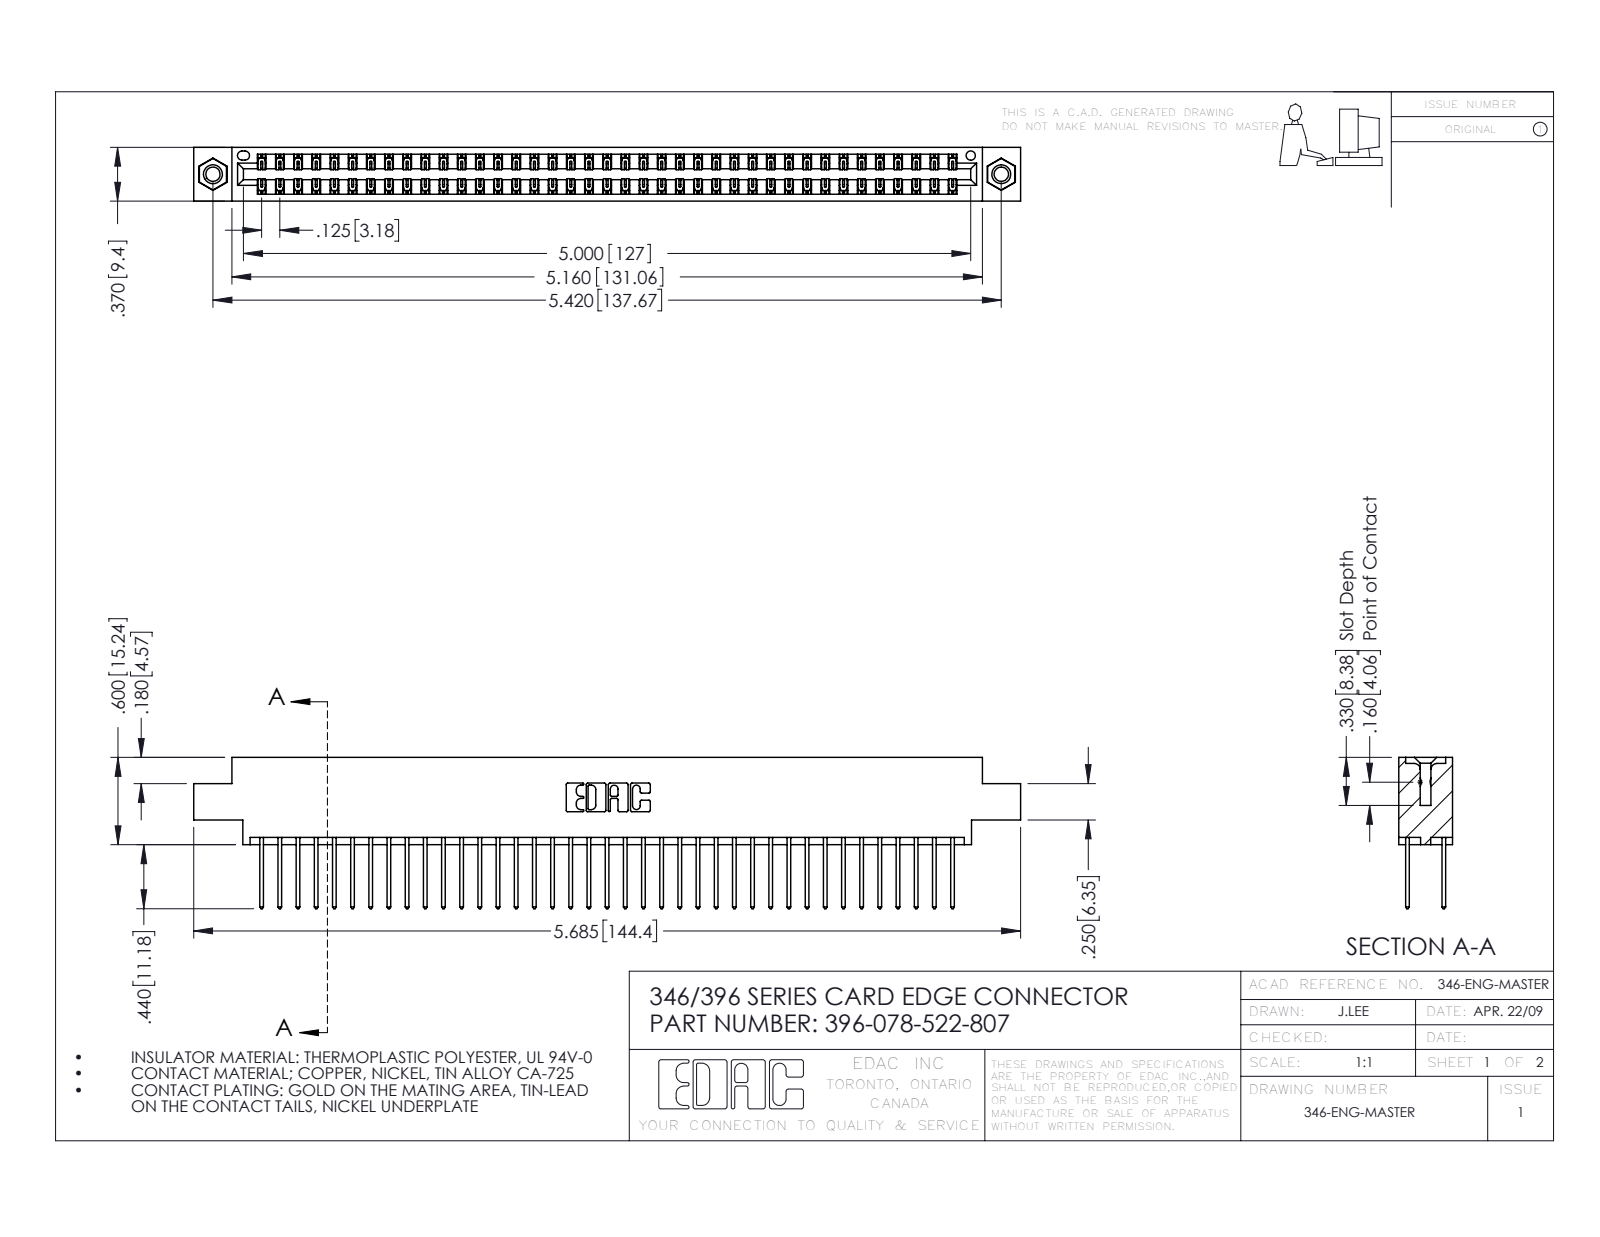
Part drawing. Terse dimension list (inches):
name: 345-292-001_345-293-122; 396-078-522-807; 346 Part_0.170 Offset - 0.156 Dia-TI; 345-250-001_345-250-005-103
written by: SolidWorks 2016 (CONFIG_CONTROL_DESIGN)
unit: in
bodies: 81 solids, 4242 faces (2842 planar, 1384 cylindrical, 16 other)
size: 5.685 × 1.04 × 0.37
volume: 0.86 in³; area: 31.71 in²
holes: 2× ⌀0.098, 2× ⌀0.125, 2× ⌀0.156, 1× ⌀0.064
bosses: 2× ⌀0.155
rounds: 117× R0.006, 78× R0.01, 22× R0.01, 6× R0.007, 6× R0.031, 3× R0.026, 2× R0.014, 2× R0.022
face distances: 0.048, 0.322, 0.25, 0.37, 0.072, 0.298, 0.025, 0.275, 0.222, 0.148
hole spacings: 0.246, 5.211, 5.42
